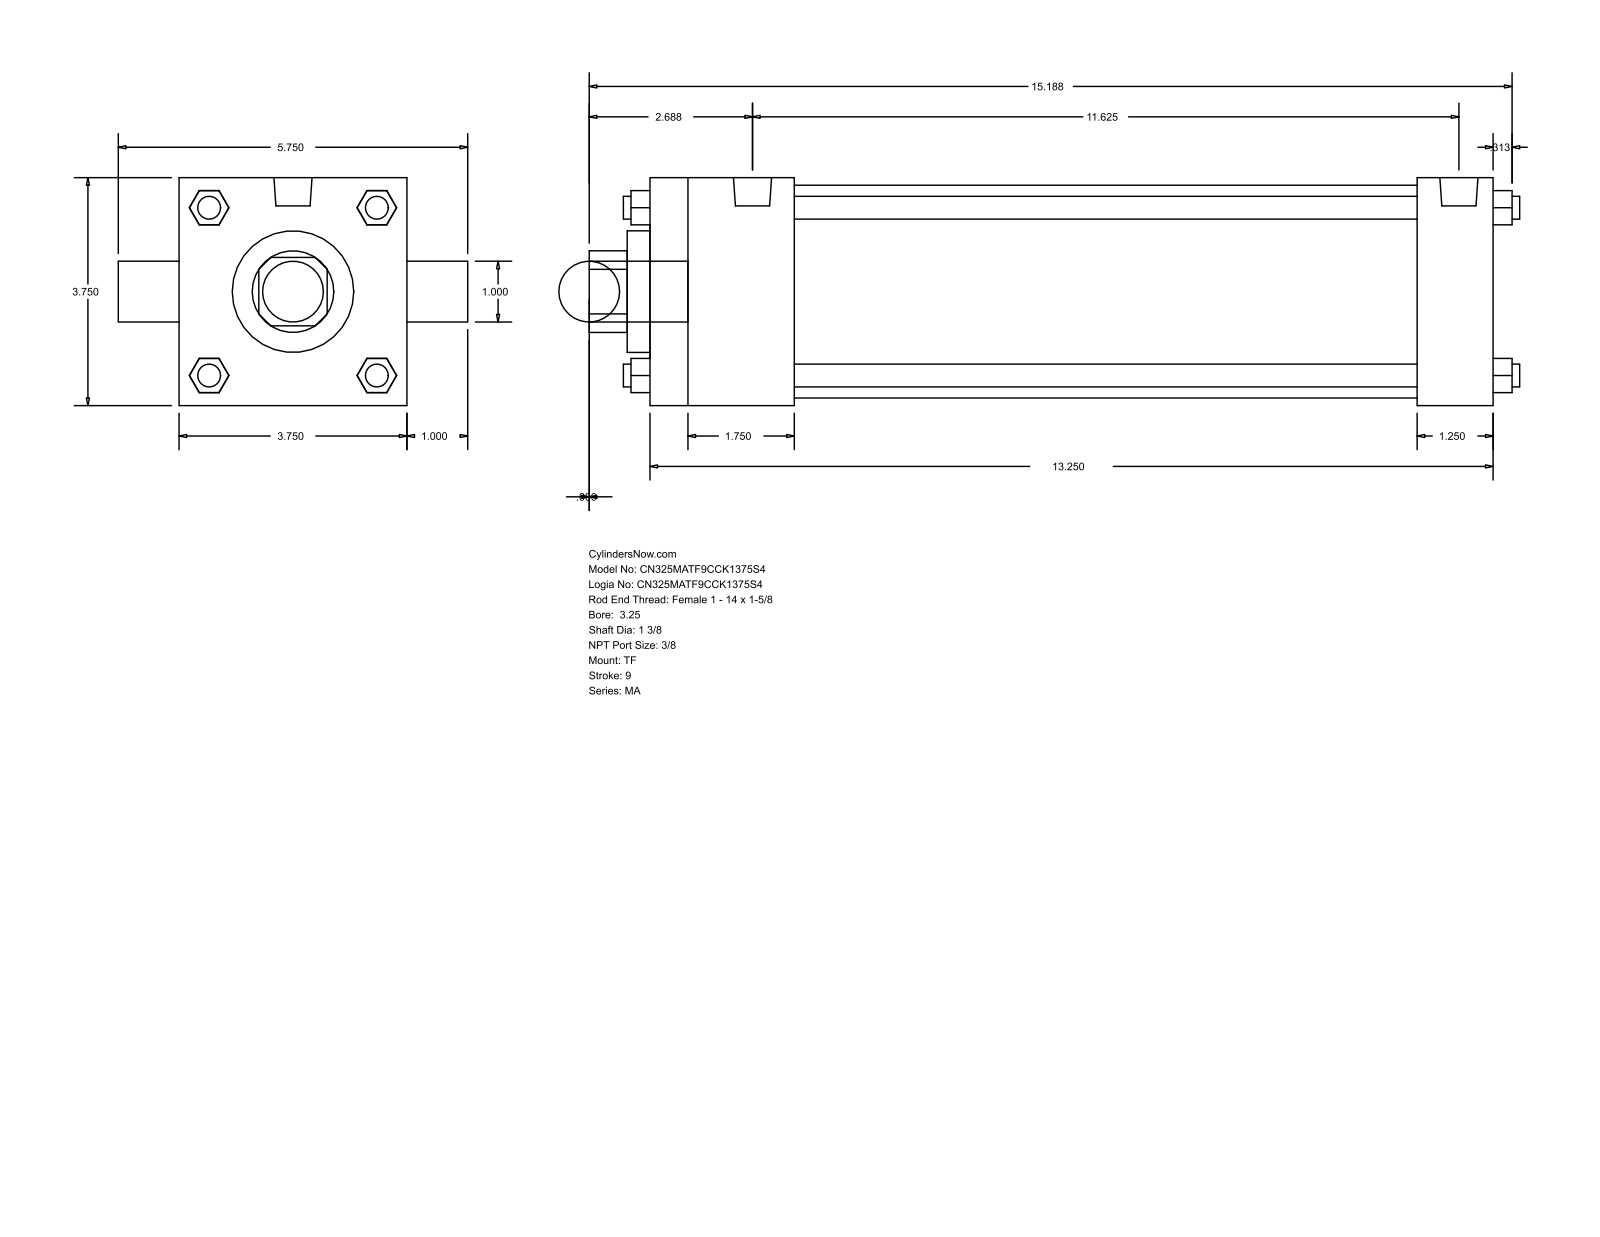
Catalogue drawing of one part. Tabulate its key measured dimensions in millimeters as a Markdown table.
| quantity | value |
| --- | --- |
| part name | MA_TF__0325_1.375 |
| STEP written by | GSSL Pune (CONFIG_CONTROL_DESIGN) |
| units | millimeters |
| bodies | 0 solids, 120 faces (92 planar, 28 cylindrical, 0 other) |
| overall size | 388.94 × 146.05 × 95.25 |
| round holes (diameter × count) | 25.4 × 1, 34.92 × 1, 50.8 × 1, 88.9 × 1 |
| round bosses / shafts (diameter × count) | 9.53 × 4, 11.11 × 3, 15.93 × 2, 25.4 × 1 |
| partial cylindrical surfaces (radius × count) | 17.06 × 1 |
| main face-to-face distances | 95.24, 352.42, 60.32, 320.67, 260.35, 292.1, 31.75, 9.52, 69.84, 330.19 |
